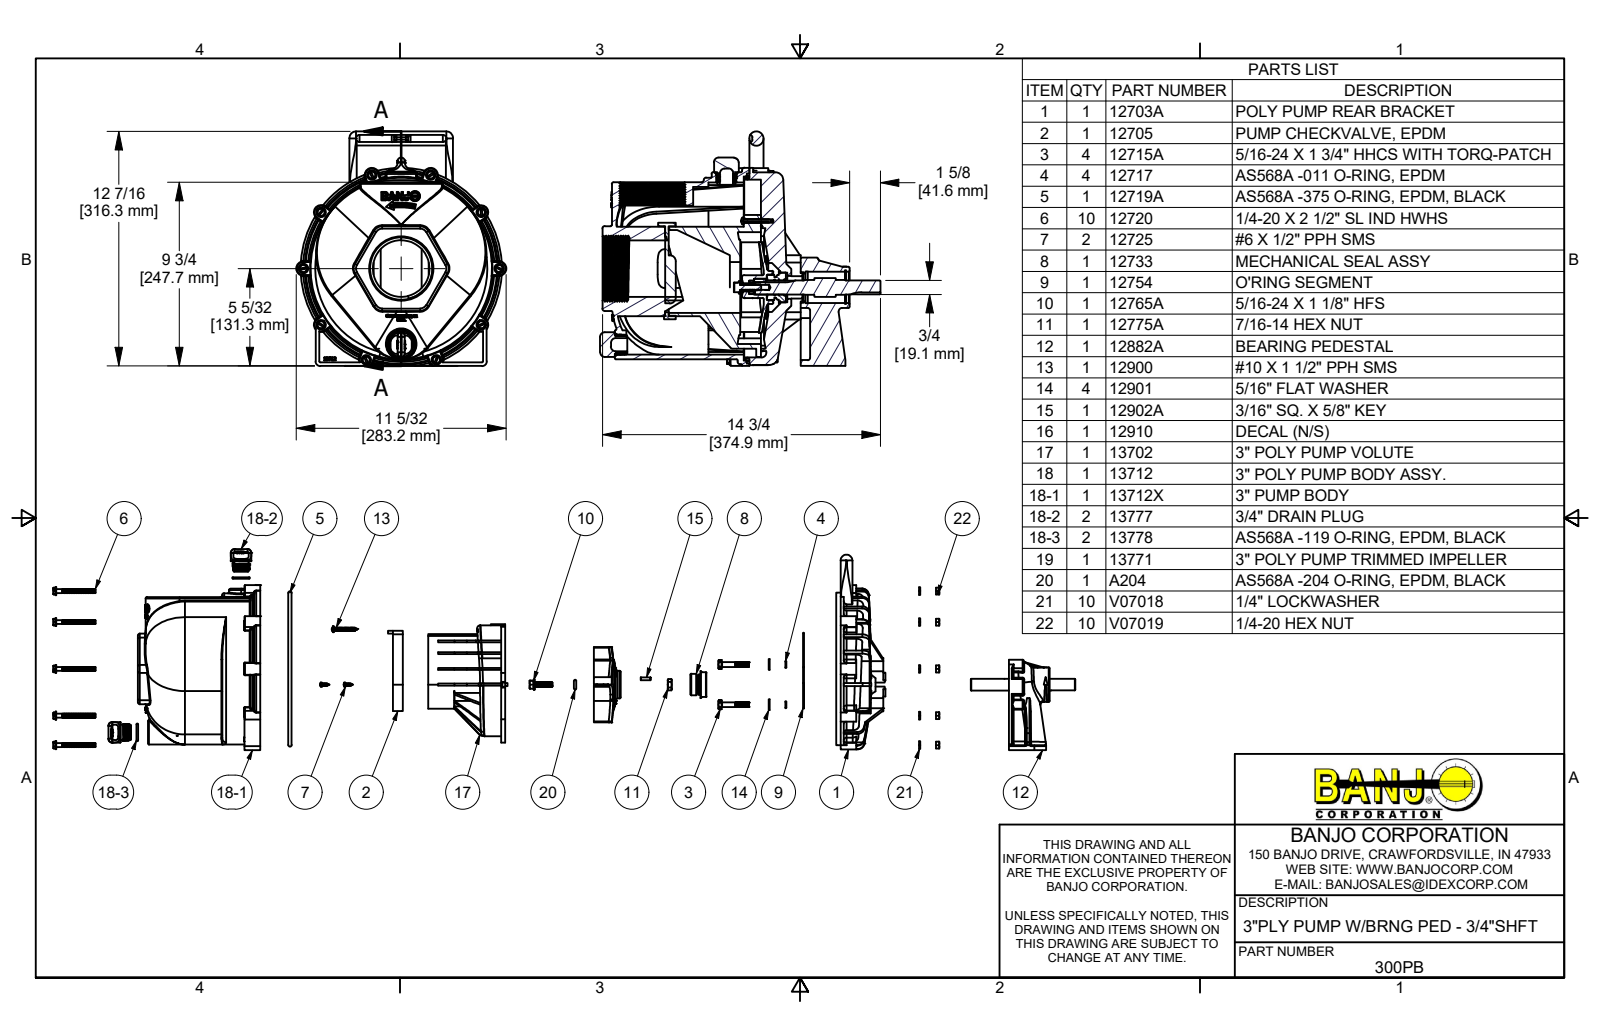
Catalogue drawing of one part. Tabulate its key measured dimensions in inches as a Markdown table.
| quantity | value |
| --- | --- |
| part name | 300PB; 12703A; 13712; 13712X (+8 more) |
| STEP written by | Autodesk Inventor 2019 (AUTOMOTIVE_DESIGN) |
| units | inches |
| bodies | 83 solids, 8137 faces (1937 planar, 2307 cylindrical, 3893 other) |
| overall size | 14.891 × 12.452 × 11.15 |
| volume | 220.1 in³ |
| surface area | 2 042 in² |
| round holes (diameter × count) | 0.196 × 10, 0.252 × 10, 0.27 × 10, 0.22 × 7, 0.267 × 5, 0.344 × 4, 0.406 × 4, 0.469 × 4, 0.815 × 4, 0.078 × 2, 0.113 × 2, 0.115 × 2 |
| round bosses / shafts (diameter × count) | 0.276 × 80, 0.52 × 10, 0.489 × 10, 0.25 × 10, 0.192 × 8, 0.688 × 4, 0.313 × 4, 1.31 × 2 |
| partial cylindrical surfaces (radius × count) | 0.03 × 116, 0.06 × 79, 0.125 × 32, 0.25 × 29, 0.187 × 25, 0.015 × 20, 0.375 × 16, 0.094 × 12 |
| main face-to-face distances | 0.25, 0.2, 1, 0.125, 0.163, 0.61, 0.19, 0.037, 0.18, 2.78 |
| hole center spacings | 5.2, 6.15, 3.127, 10.4, 1.563, 1.81, 1.81, 2.559 |
